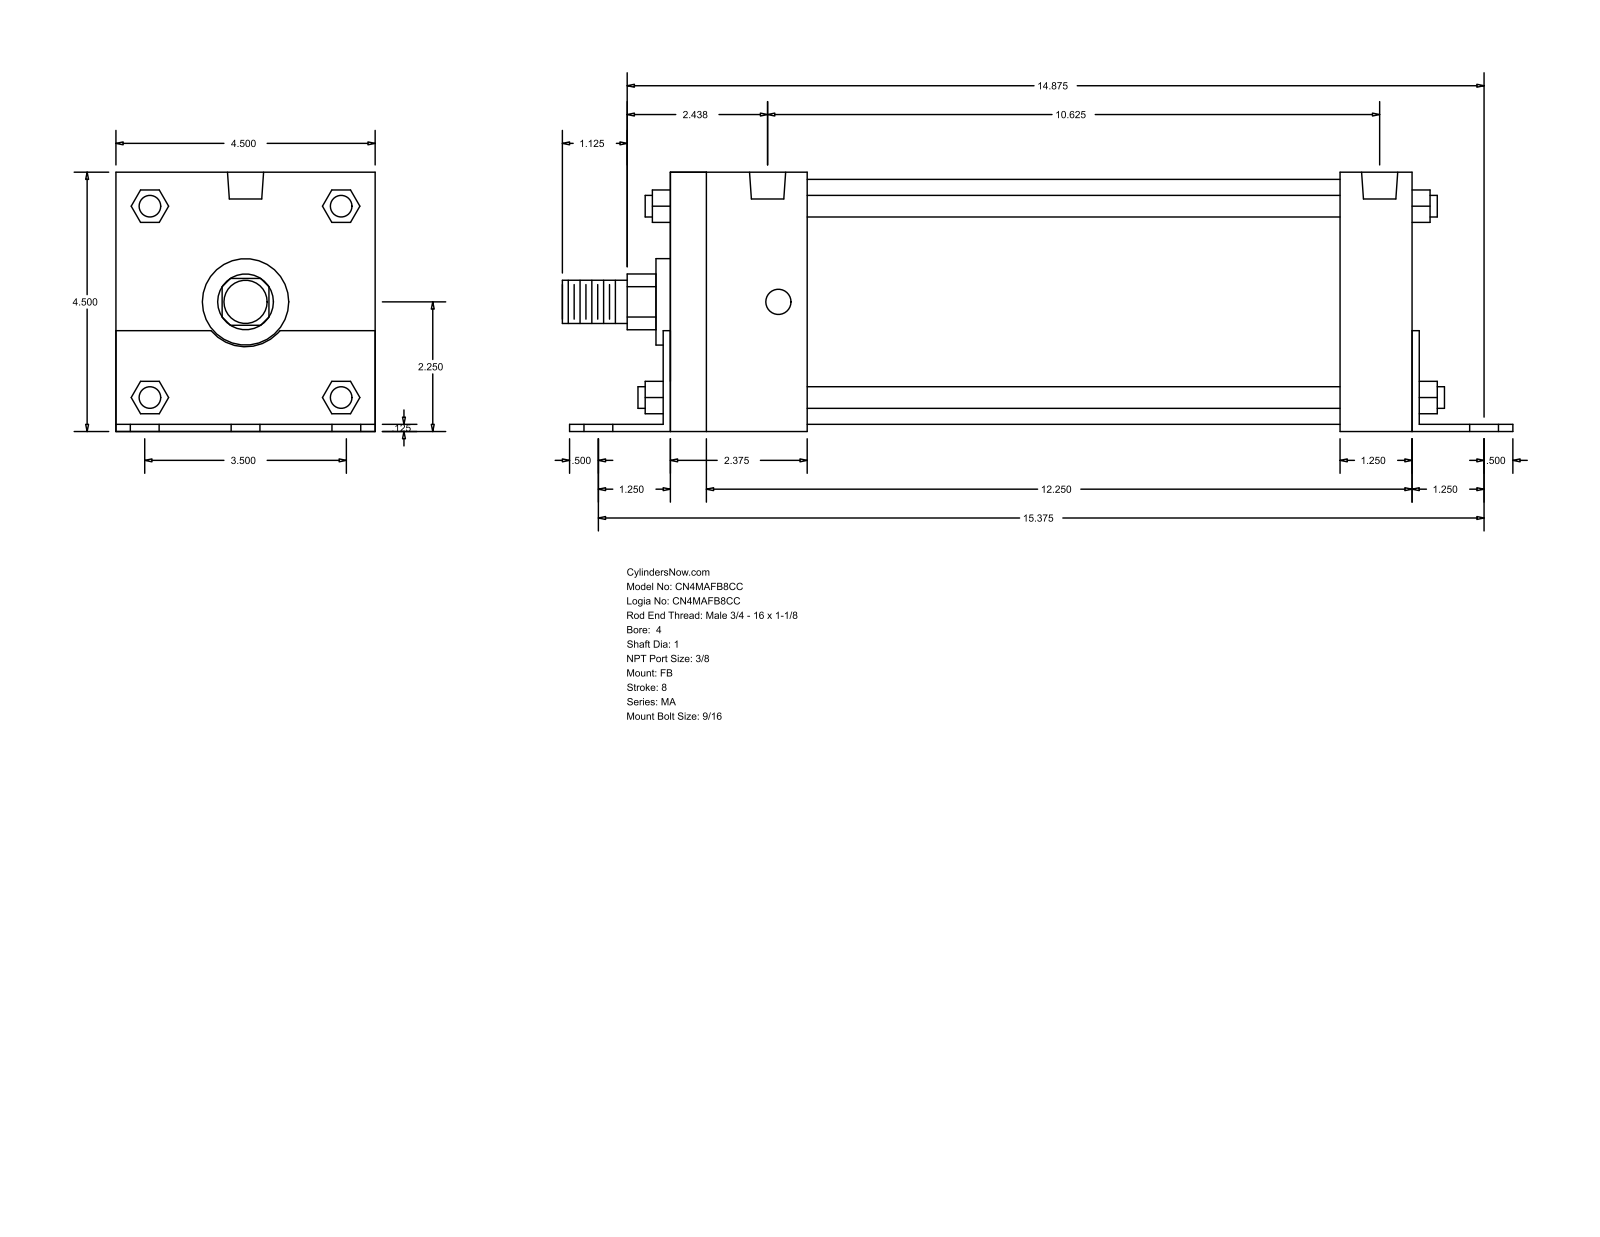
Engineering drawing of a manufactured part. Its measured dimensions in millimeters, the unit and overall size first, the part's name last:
Units: millimetres
Overall size (bounding box): 419.1 × 114.35 × 114.3
Round holes (diameter × count): ⌀14.29 ×6, ⌀11.11 ×4, ⌀15.93 ×2
Round bosses / shafts (diameter × count): ⌀9.53 ×4, ⌀107.95 ×1, ⌀38.1 ×1, ⌀25.4 ×1, ⌀19.05 ×1
Partial cylindrical surfaces — rounded edges, fillets, slot ends (radius × count): R12.29 ×1, R19.81 ×1
Main face-to-face distances: 114.3, 3.17, 114.35, 3.12, 111.18, 327.02, 3.18, 333.37, 330.2, 330.19
Hole centre spacings: 44.45, 393.04, 390.52, 63.99, 67.5, 86.85, 88.9, 90.97
Bodies: 0 solids, 140 faces (105 planar, 35 cylindrical, 0 other)
Part name (STEP PRODUCT): MA_FB__0400_1
STEP written by: GSSL Pune (CONFIG_CONTROL_DESIGN)
